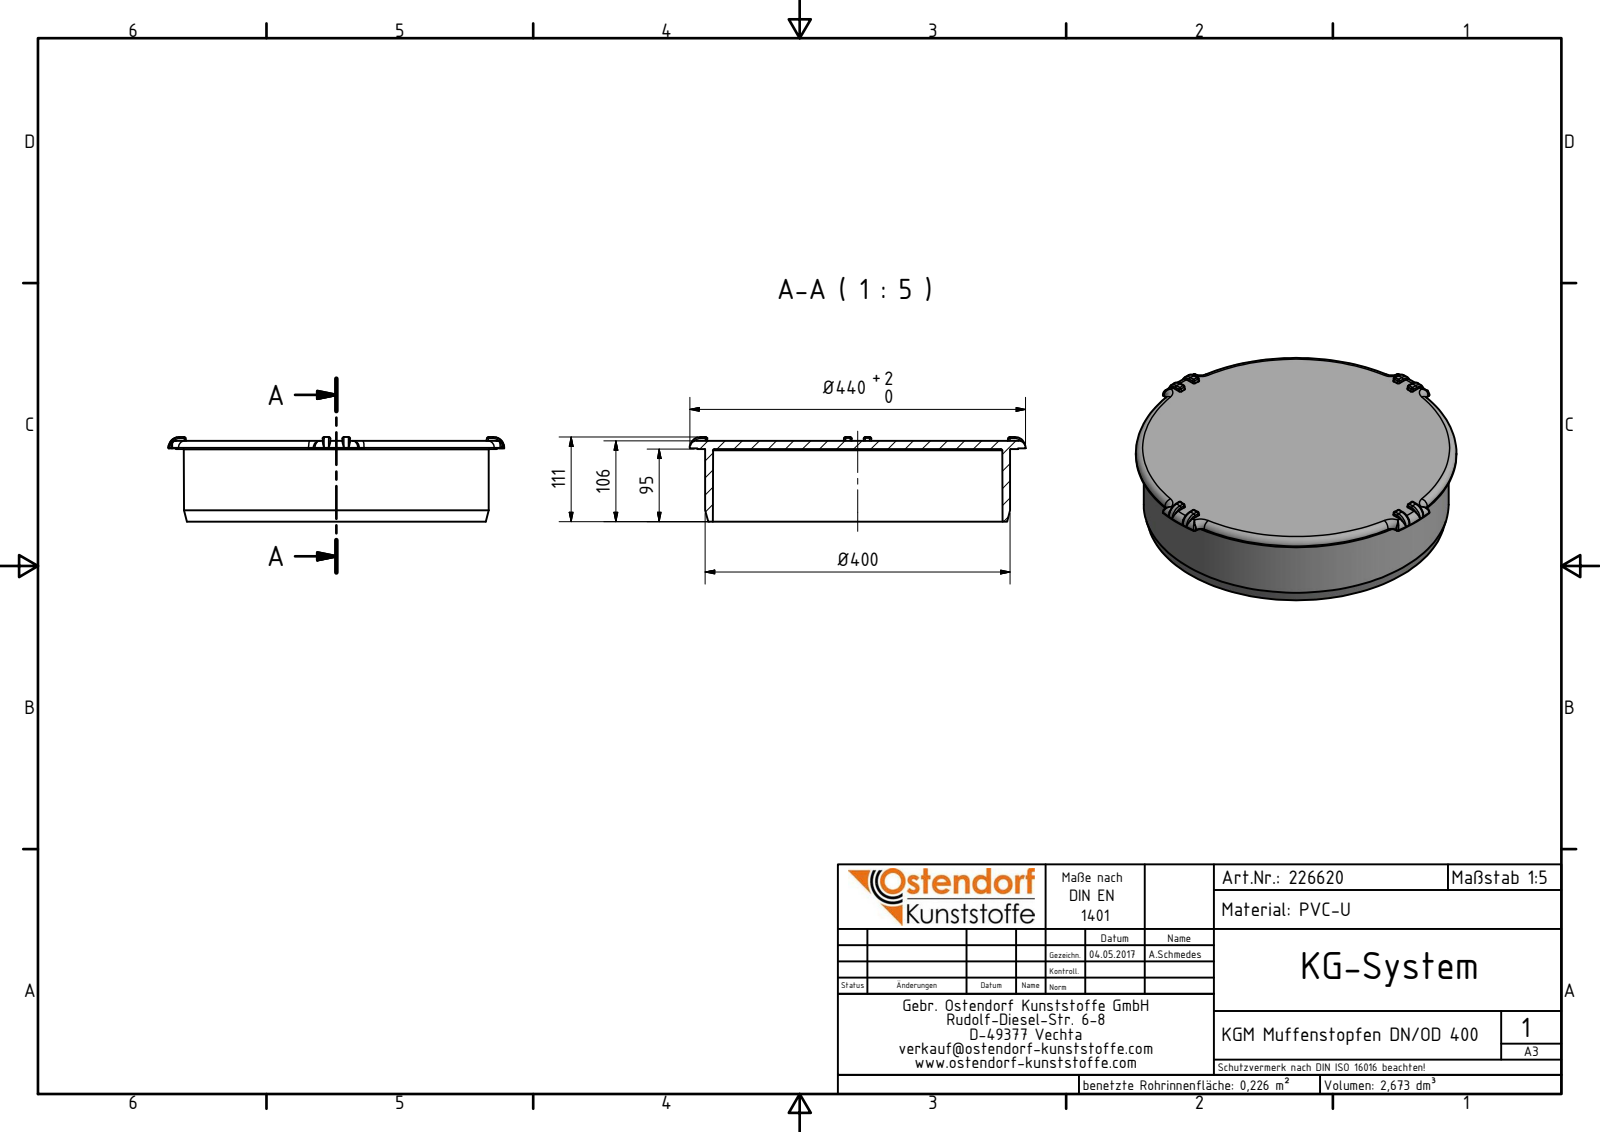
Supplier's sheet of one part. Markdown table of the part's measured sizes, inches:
| quantity | value |
| --- | --- |
| part name | 226620 KGM Muffenstopfen DN_OD 400 neu mit Ohren |
| STEP written by | Autodesk Inventor 2016 (AUTOMOTIVE_DESIGN) |
| units | inches |
| bodies | 1 solid, 202 faces (40 planar, 45 cylindrical, 117 other) |
| overall size | 17.355 × 17.355 × 4.378 |
| volume | 163.1 in³ |
| surface area | 808.8 in² |
| round bosses / shafts (diameter × count) | 16.572 × 1 |
| partial cylindrical surfaces (radius × count) | 0.078 × 16, 0.313 × 8, 0.352 × 4, 0.352 × 3, 8.678 × 1 |
| main face-to-face distances | 0.431, 3.751, 4.181, 0.391, 3.79, 0.039, 0.626, 4.377, 0.587, 0.196 |
